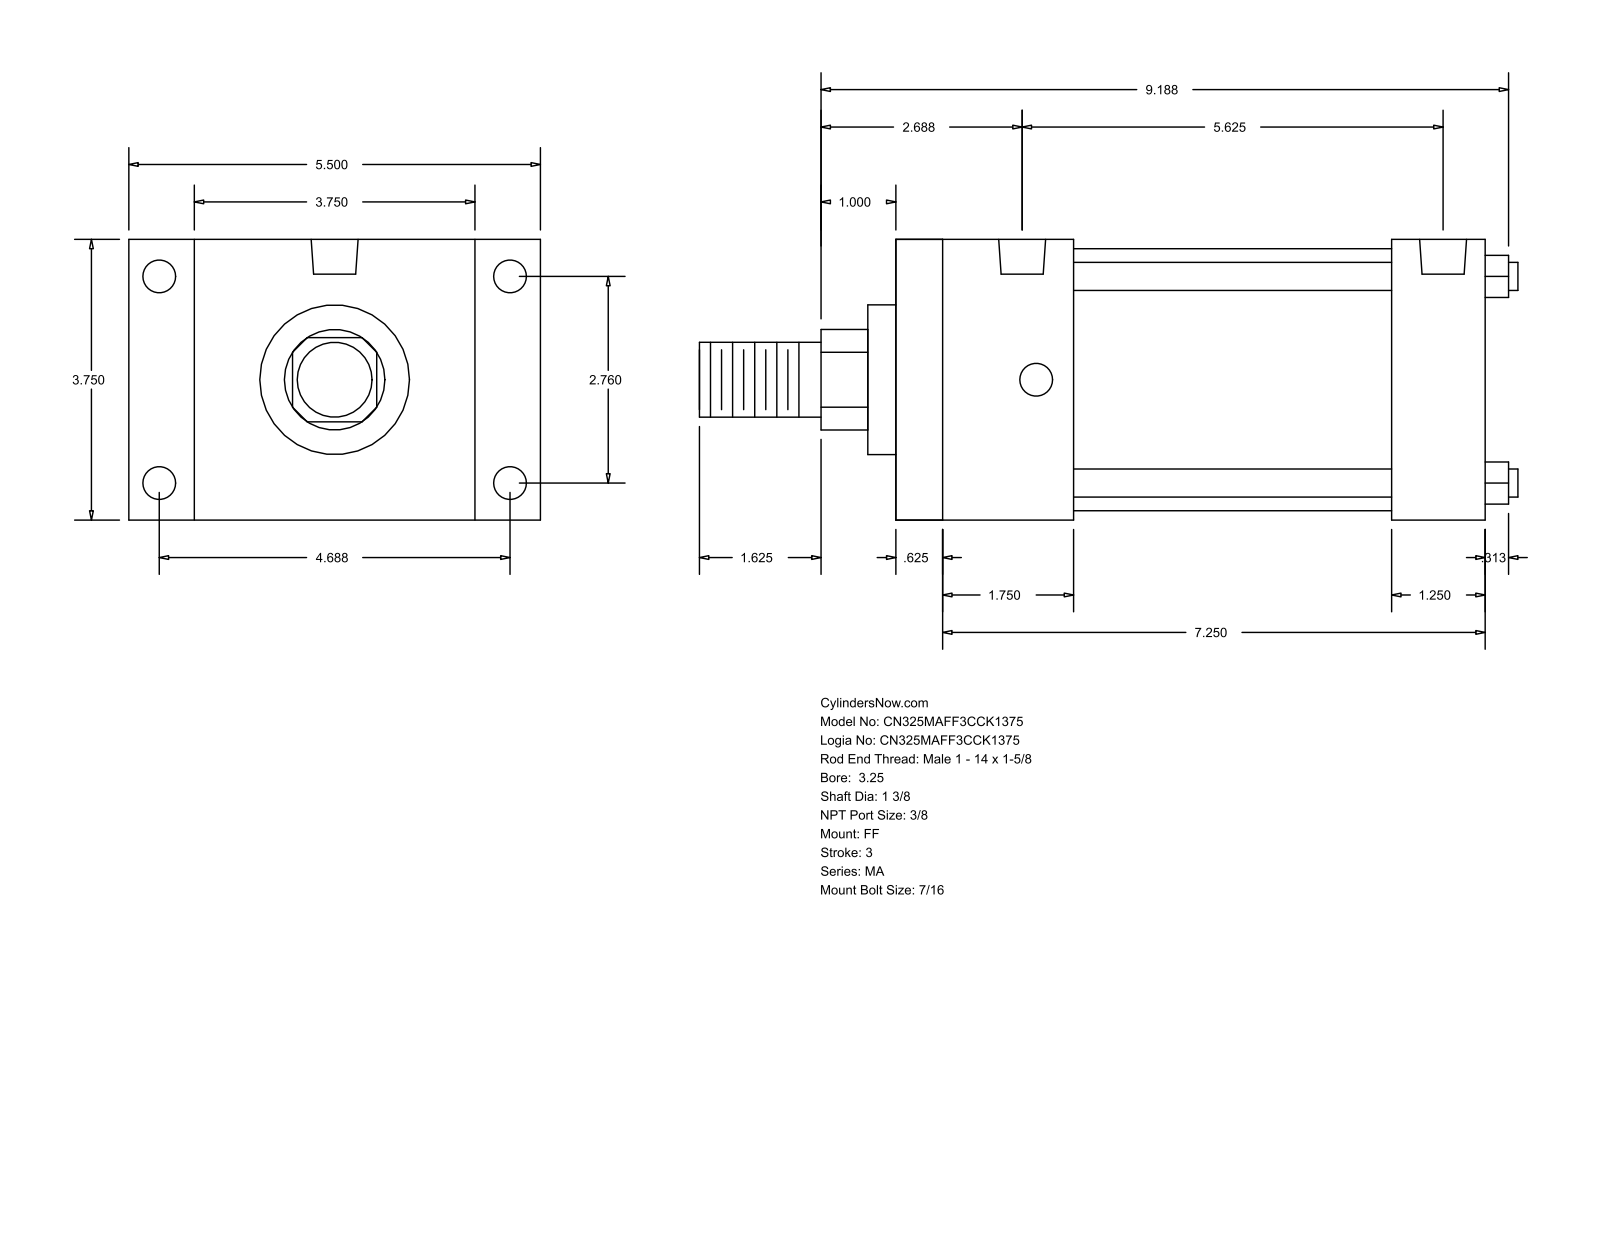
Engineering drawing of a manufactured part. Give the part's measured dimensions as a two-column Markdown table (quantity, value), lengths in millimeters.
| quantity | value |
| --- | --- |
| part name | MA_FF__0325_1.375 |
| STEP written by | GSSL Pune (CONFIG_CONTROL_DESIGN) |
| units | millimeters |
| bodies | 0 solids, 92 faces (64 planar, 28 cylindrical, 0 other) |
| overall size | 277.81 × 139.7 × 95.25 |
| round holes (diameter × count) | 11.11 × 8, 15.93 × 2 |
| round bosses / shafts (diameter × count) | 9.53 × 4, 88.9 × 1, 50.8 × 1, 34.92 × 1, 25.4 × 1 |
| partial cylindrical surfaces (radius × count) | 17.06 × 1 |
| main face-to-face distances | 95.24, 200.03, 15.87, 184.16, 22.23, 117.47, 60.32, 168.28, 44.45, 152.41 |
| hole center spacings | 70.1, 119.06, 133.35, 138.16, 4.76, 4.77, 138.11, 138.12 |
